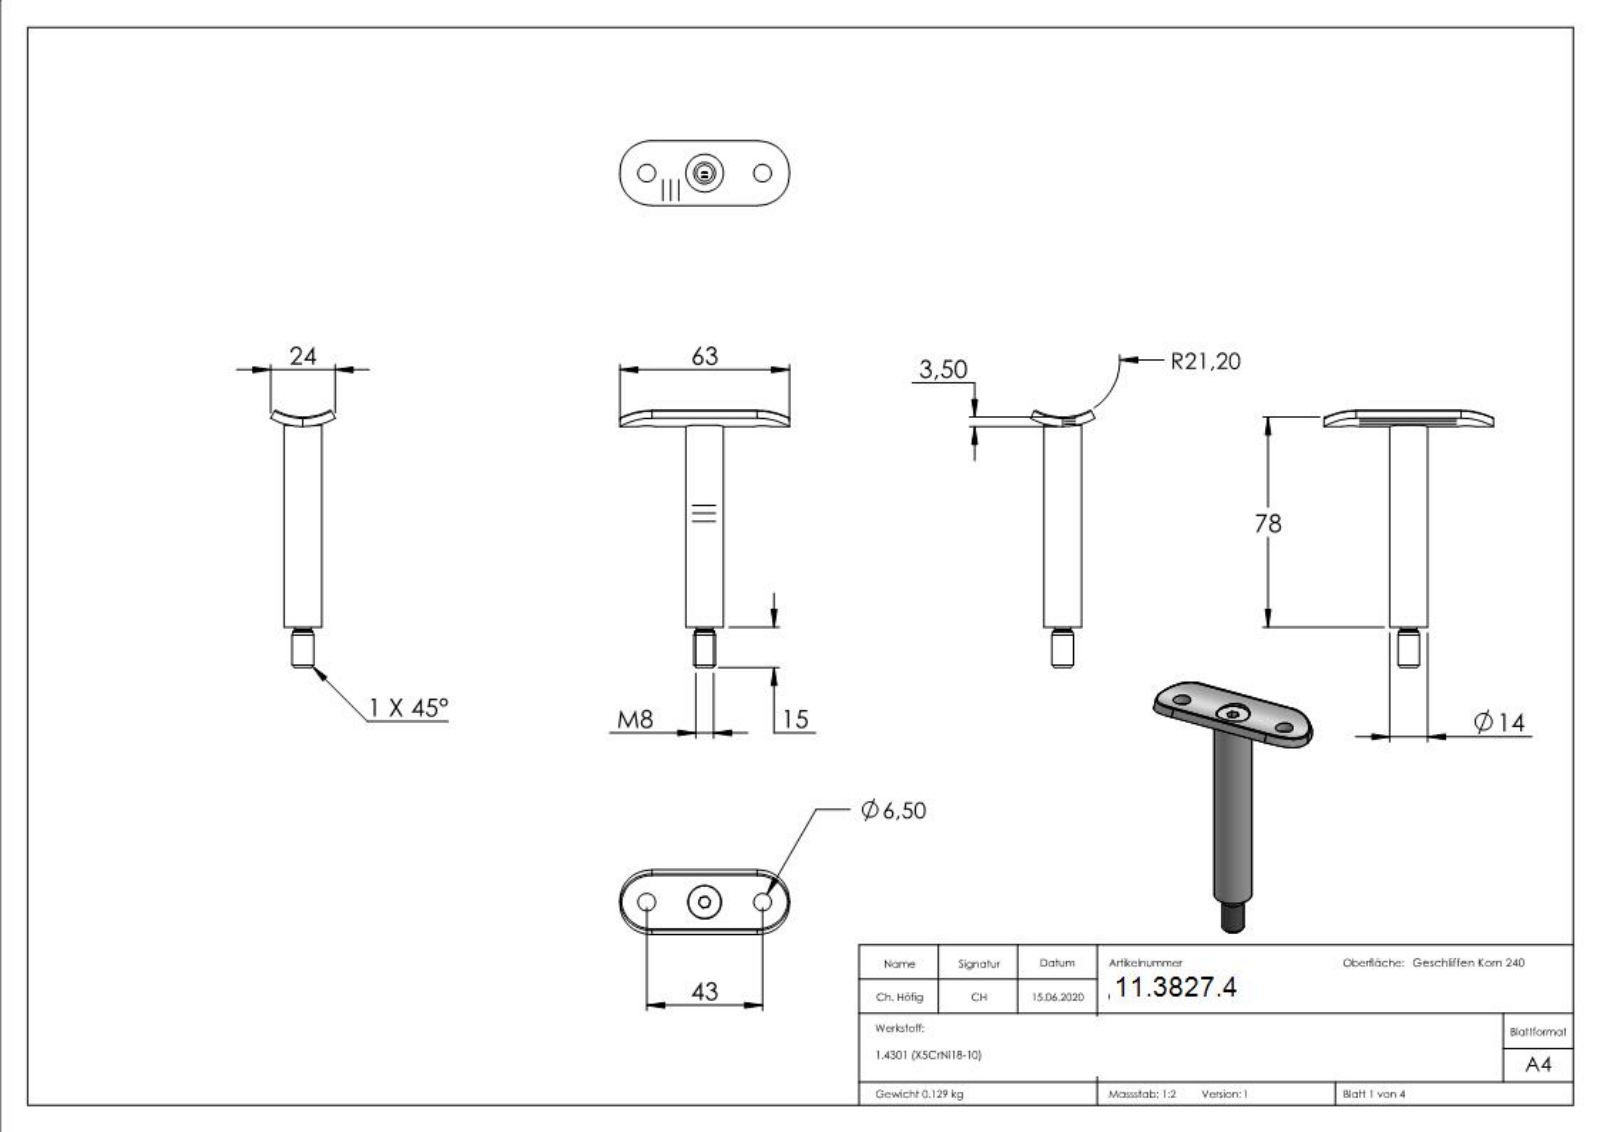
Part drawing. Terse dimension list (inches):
name: 60182-240_60182-240; 50236-Konfig_50233-240; 60172-240; 60182-240 (+3 more)
written by: SolidWorks 2015 (CONFIG_CONTROL_DESIGN)
unit: in
bodies: 3 solids, 264 faces (136 planar, 20 cylindrical, 108 other)
size: 3.799 × 2.48 × 0.945
volume: 0.999 in³; area: 12.42 in²
holes: 2× ⌀0.256, 1× ⌀0.197, 1× ⌀0.315, 1× ⌀0.492, 1× ⌀0.551
bosses: 1× ⌀0.472, 1× ⌀0.236
rounds: 4× R0.472, 2× R0.02, 1× R0.835, 1× R0.972
face distances: 0.11, 3.543, 3.654, 0.157, 3.024, 0.52, 0.63, 3.535, 0.512, 0.118
hole spacings: 0.846, 1.693
